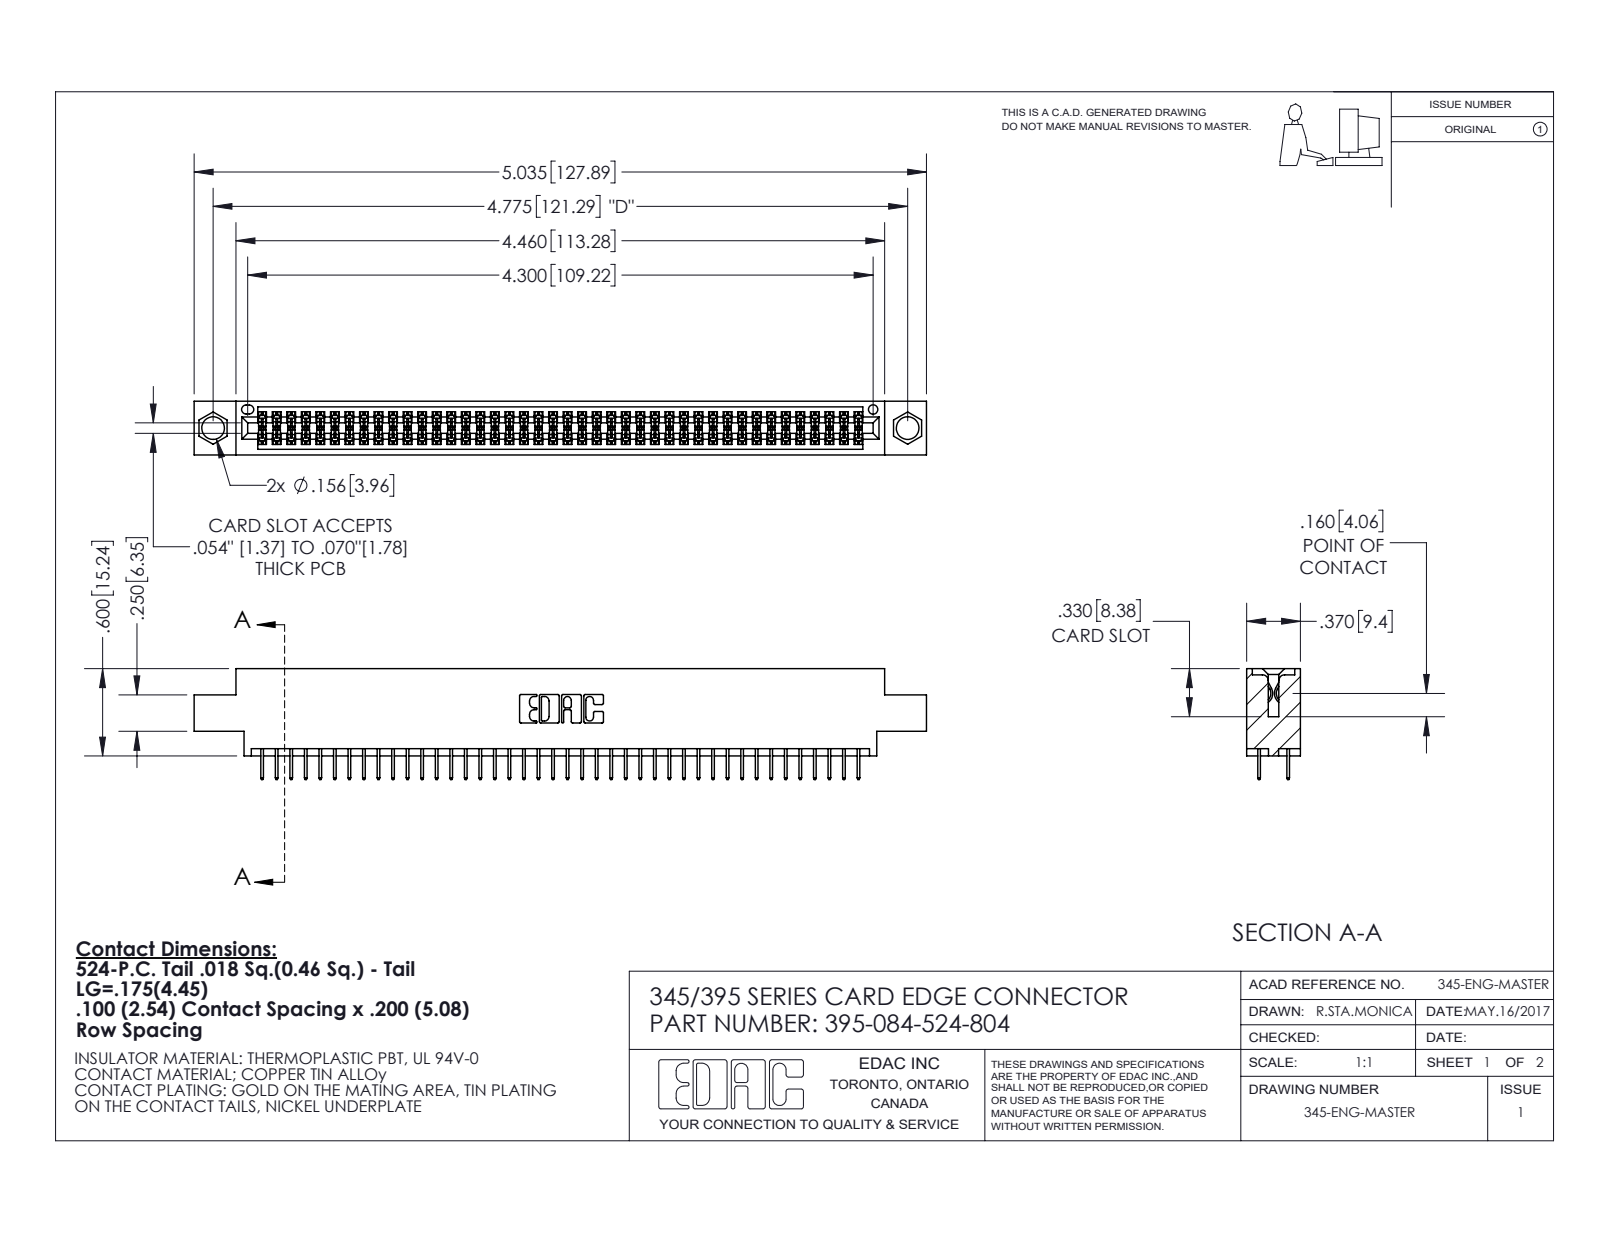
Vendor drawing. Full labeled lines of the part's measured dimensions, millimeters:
Part name (STEP PRODUCT): 345-292-001_345-293-124; 395-084-524-804; 345 Part_0.170 Offset - 0.156 Dia-TI
STEP written by: SolidWorks 2020 (CONFIG_CONTROL_DESIGN)
Units: millimetres
Bodies: 85 solids, 4680 faces (3374 planar, 1306 cylindrical, 0 other)
Overall size (bounding box): 127.9 × 19.4 × 9.4
Volume: 12 100 mm³ · Surface area: 17 510 mm²
Round holes (diameter × count): ⌀4 ×2, ⌀1.6 ×1
Partial cylindrical surfaces — rounded edges, fillets, slot ends (radius × count): R0.2 ×126, R0.3 ×22, R0.2 ×6, R0.8 ×6, R0.7 ×3, R0.4 ×2, R0.5 ×2, R0.6 ×2
Main face-to-face distances: 1.8, 7.6, 5.1, 9.4, 2.5, 6.9, 0.6, 5.7, 4.4, 1.8
Hole centre spacings: 6.9, 115.3, 121.3
